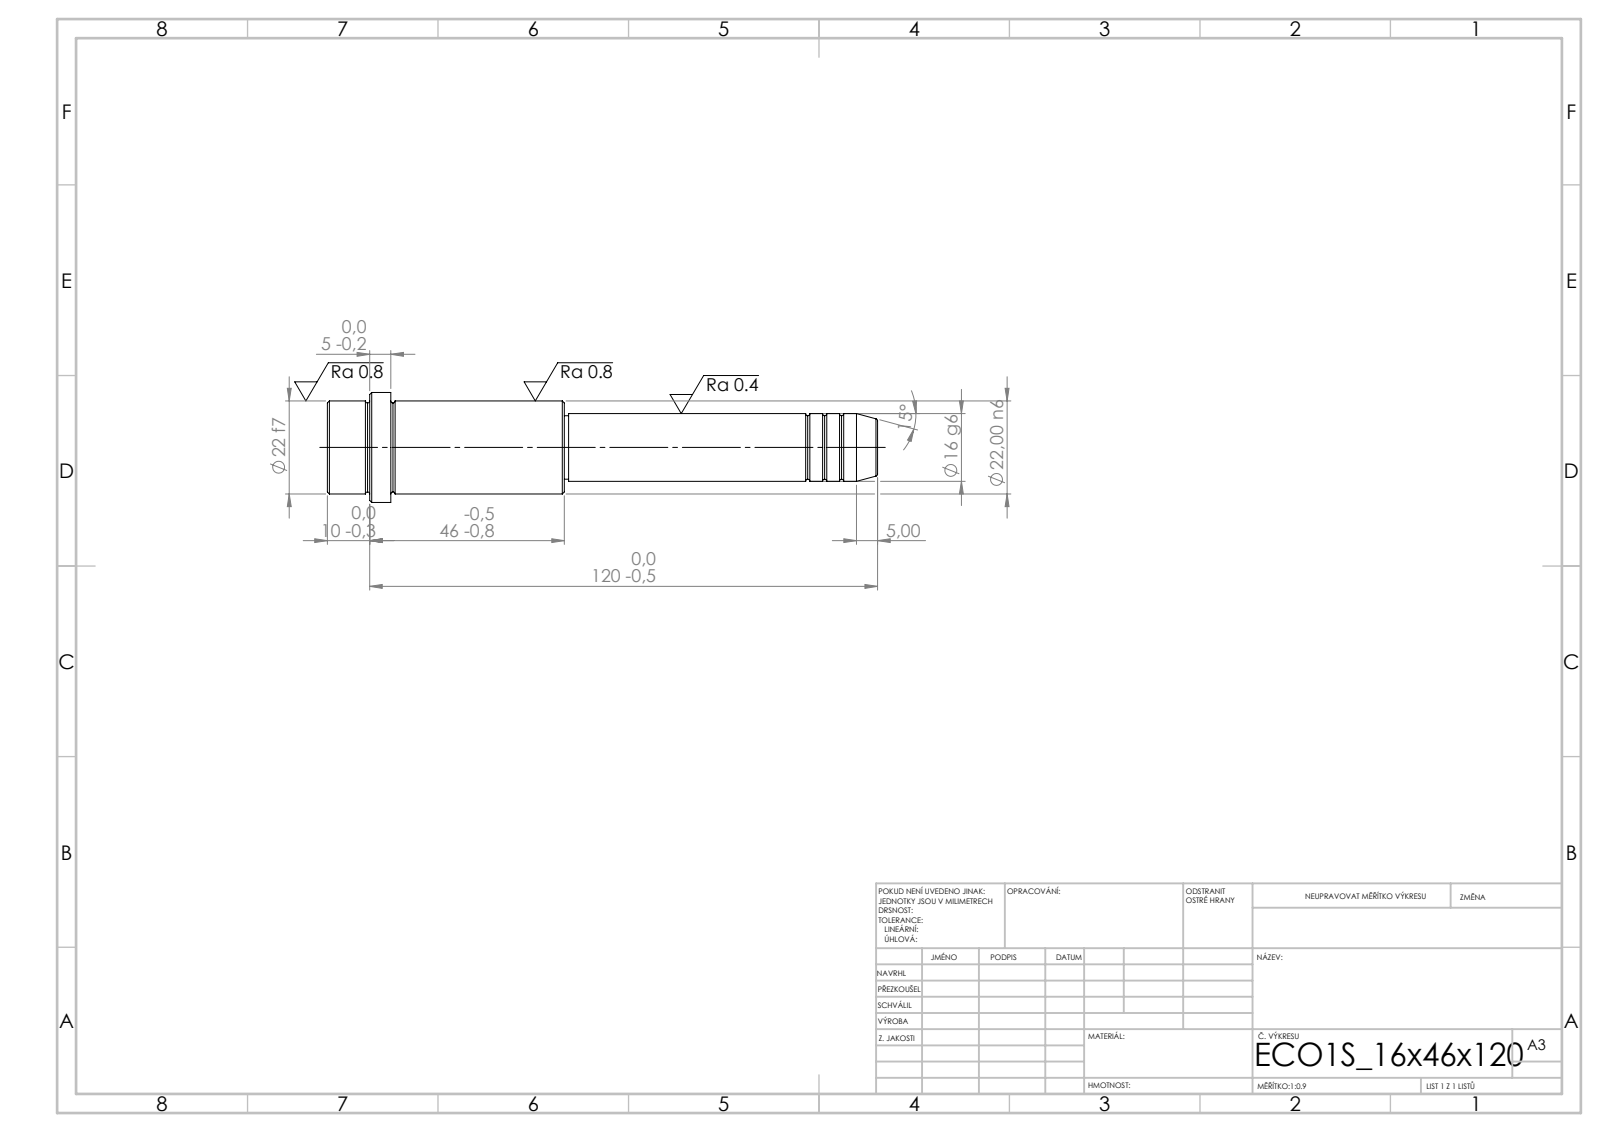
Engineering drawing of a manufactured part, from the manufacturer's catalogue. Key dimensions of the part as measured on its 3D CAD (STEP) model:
STEP written by: SolidWorks 2019 (CONFIG_CONTROL_DESIGN)
Units: millimetres
Bodies: 1 solid, 52 faces (6 planar, 16 cylindrical, 30 other)
Overall size (bounding box): 130 × 26 × 26
Volume: 36 598 mm³ · Surface area: 8 765 mm²
Round bosses / shafts (diameter × count): ⌀26 ×1, ⌀22 ×1, ⌀16 ×1, ⌀15 ×1
Main face-to-face distances: 56, 41, 15, 74, 115, 130, 120, 46, 5, 10
